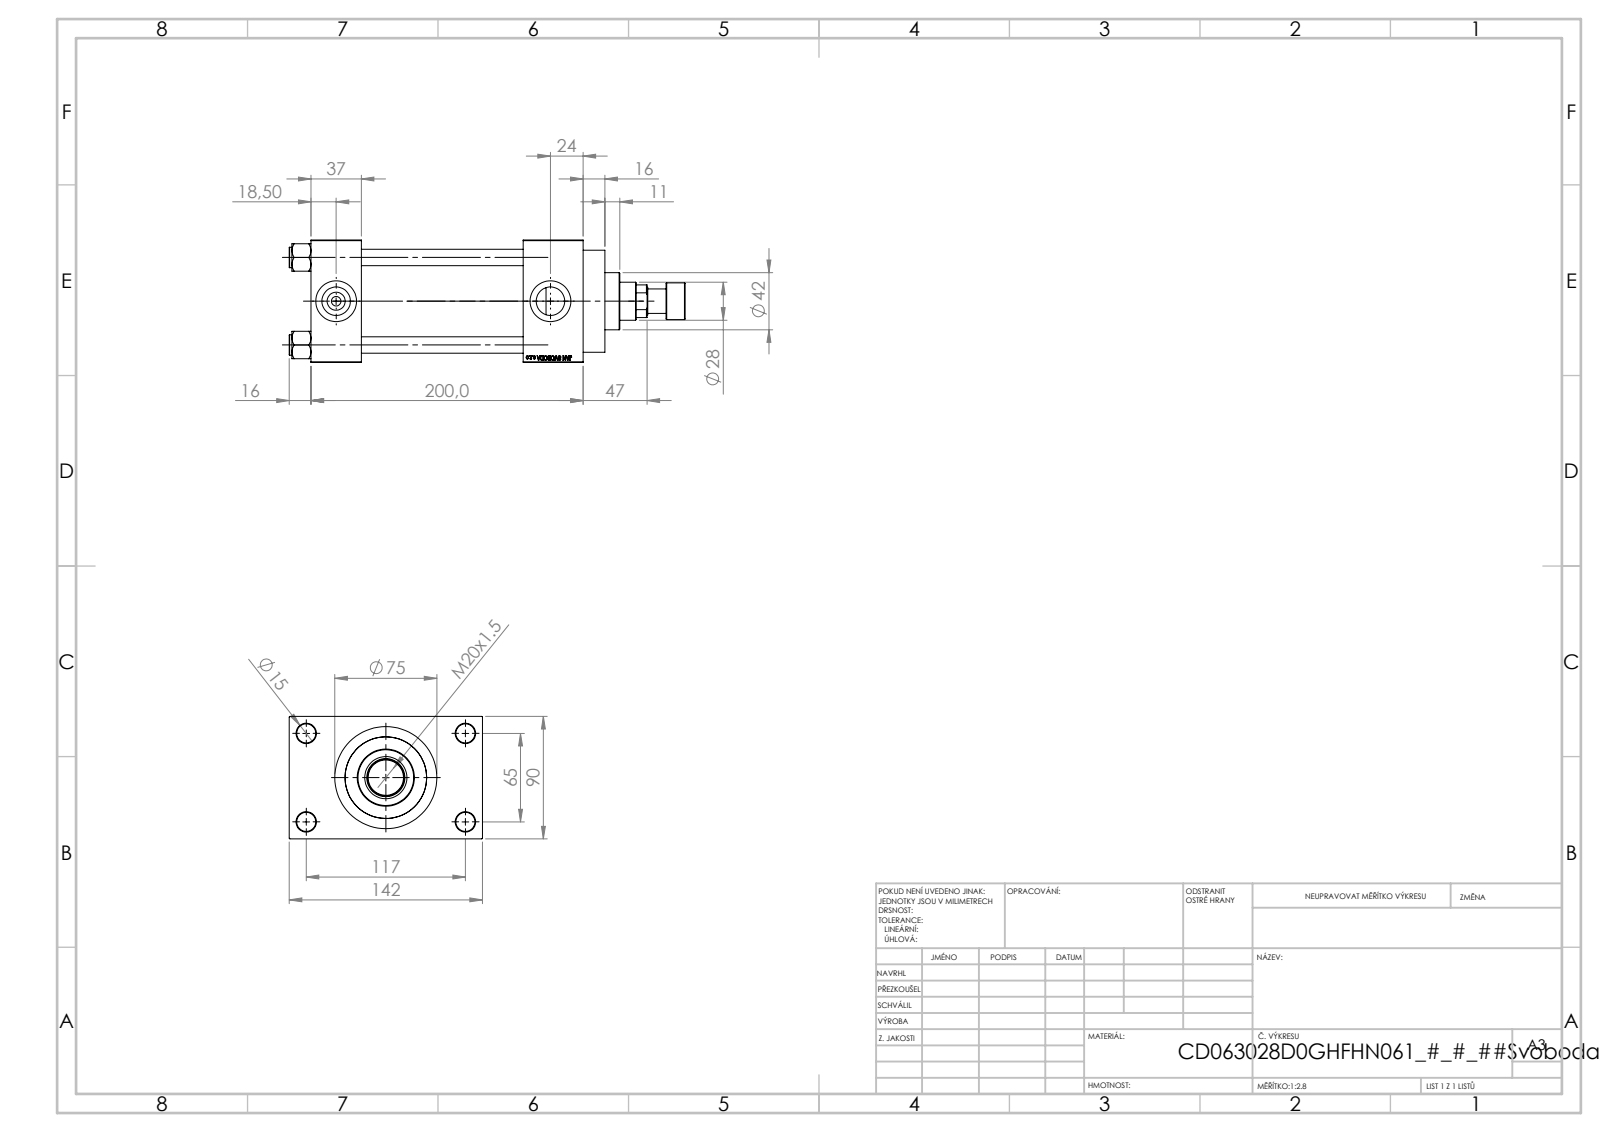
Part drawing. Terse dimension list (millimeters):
name: V215CR_ROD_END_F; V215CD_D_TYCINKA; V215CD_VC_A; V215CD_VCP_D (+2 more)
written by: SolidWorks 2019 (CONFIG_CONTROL_DESIGN)
unit: mm
bodies: 12 solids, 1117 faces (501 planar, 92 cylindrical, 524 other)
size: 291 × 142 × 90
volume: 1 209 000 mm³; area: 242 777 mm²
holes: 4× ⌀12, 4× ⌀14, 2× ⌀7, 2× ⌀20.96, 2× ⌀30, 1× ⌀18.5, 1× ⌀28, 1× ⌀31, 1× ⌀50, 1× ⌀60, 1× ⌀63
bosses: 4× ⌀15, 1× ⌀75, 1× ⌀69, 1× ⌀42, 1× ⌀27, 1× ⌀18
face distances: 90, 119, 37, 156, 163, 200, 44, 26, 116, 16
hole spacings: 26.35, 45.47, 64.3, 66.92, 69.81, 90.65, 111.34, 65
